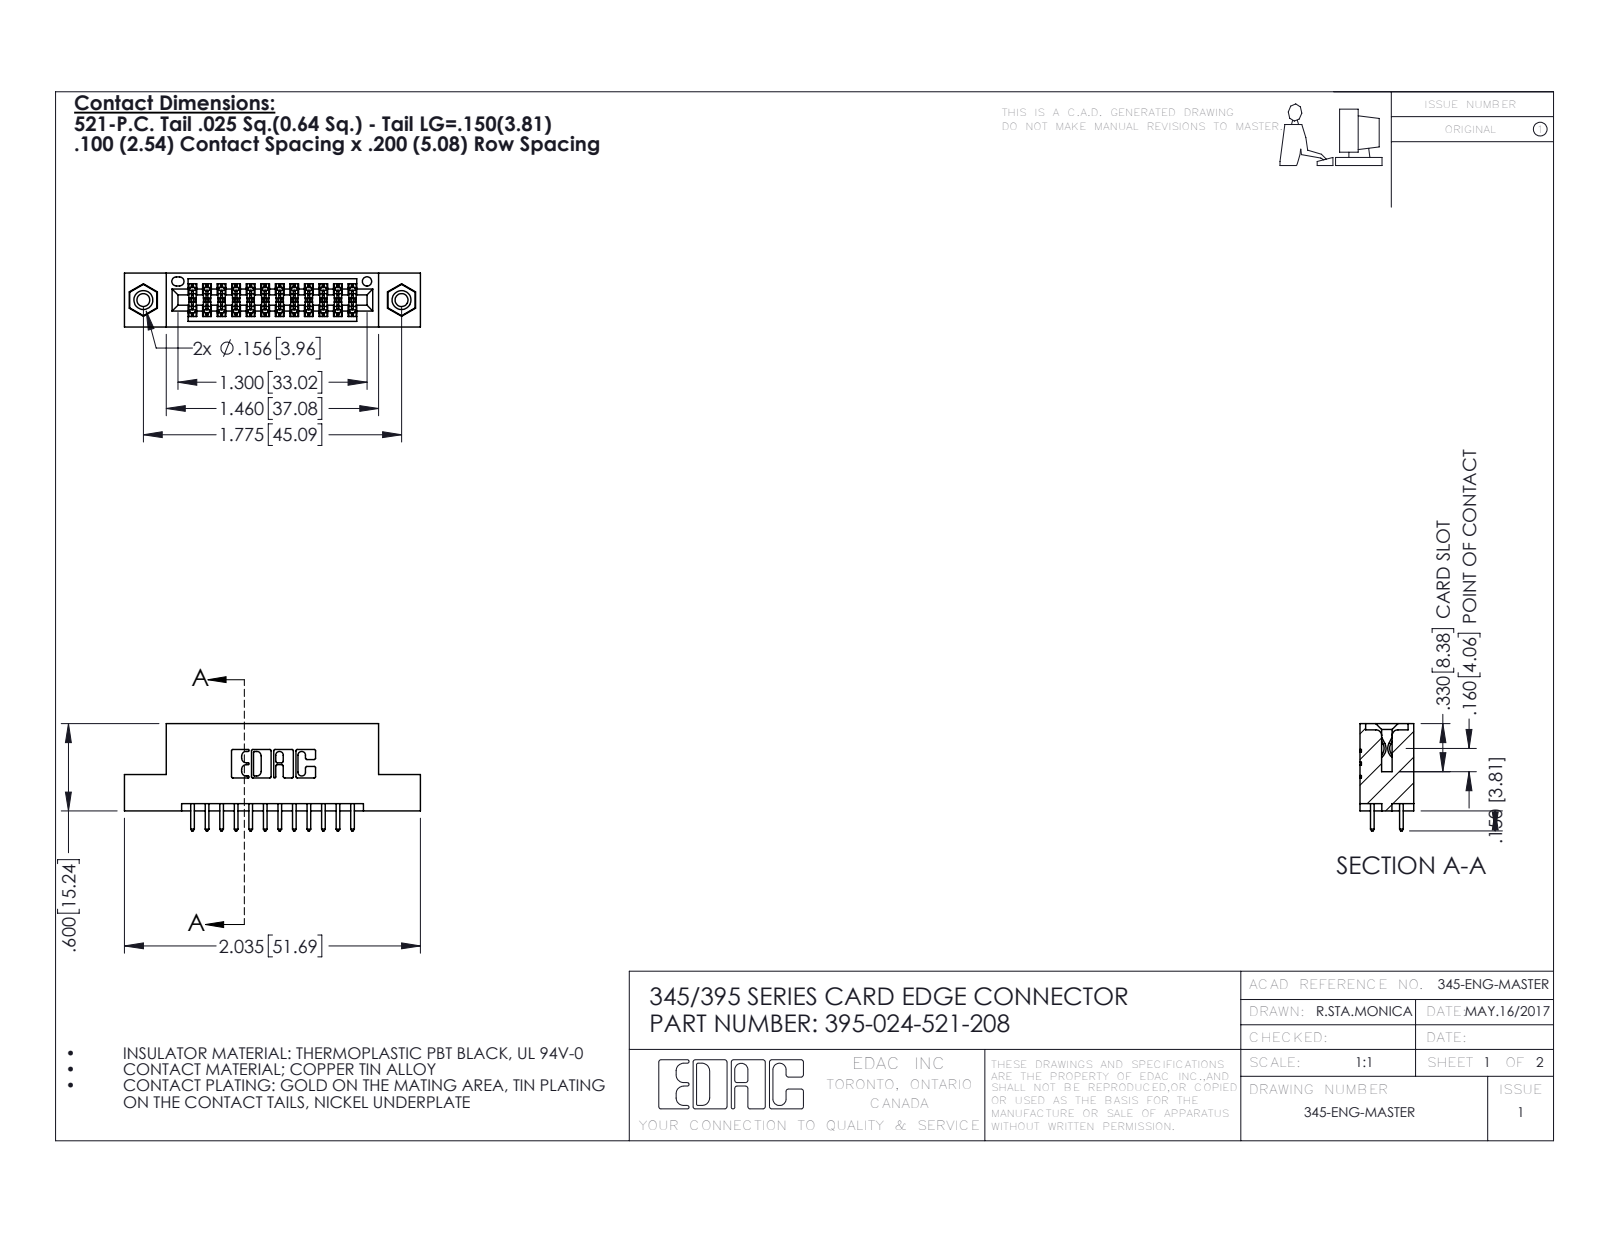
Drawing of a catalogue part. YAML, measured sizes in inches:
part_name: "395-024-521-208; 345-292-001_345-293-121; 345-250-001_345-250-003-102; 345 Part_Flush Mounting Lugs - 0.156 Dia-TI"
step_written_by: "SolidWorks 2016 (CONFIG_CONTROL_DESIGN)"
units: inches
bodies: {solids: 27, faces: 1386, planar: 904, cylindrical: 466, other: 16}
overall_size: [2.035, 0.737, 0.37]
volume: 0.288
surface_area: 9.85
round_holes:
  - {diameter: 0.089, count: 2}
  - {diameter: 0.125, count: 2}
  - {diameter: 0.156, count: 2}
  - {diameter: 0.064, count: 1}
round_bosses_or_shafts:
  - {diameter: 0.155, count: 2}
partial_cylinders:
  - {radius: 0.006, count: 36}
  - {radius: 0.01, count: 24}
  - {radius: 0.01, count: 22}
  - {radius: 0.007, count: 6}
  - {radius: 0.031, count: 6}
  - {radius: 0.026, count: 3}
  - {radius: 0.014, count: 2}
  - {radius: 0.019, count: 2}
face_to_face_distances: [0.2, 0.072, 0.298, 0.37, 0.098, 0.272, 0.025, 0.225, 0.1, 0.6]
hole_center_spacings: [0.27, 1.543, 1.775]
